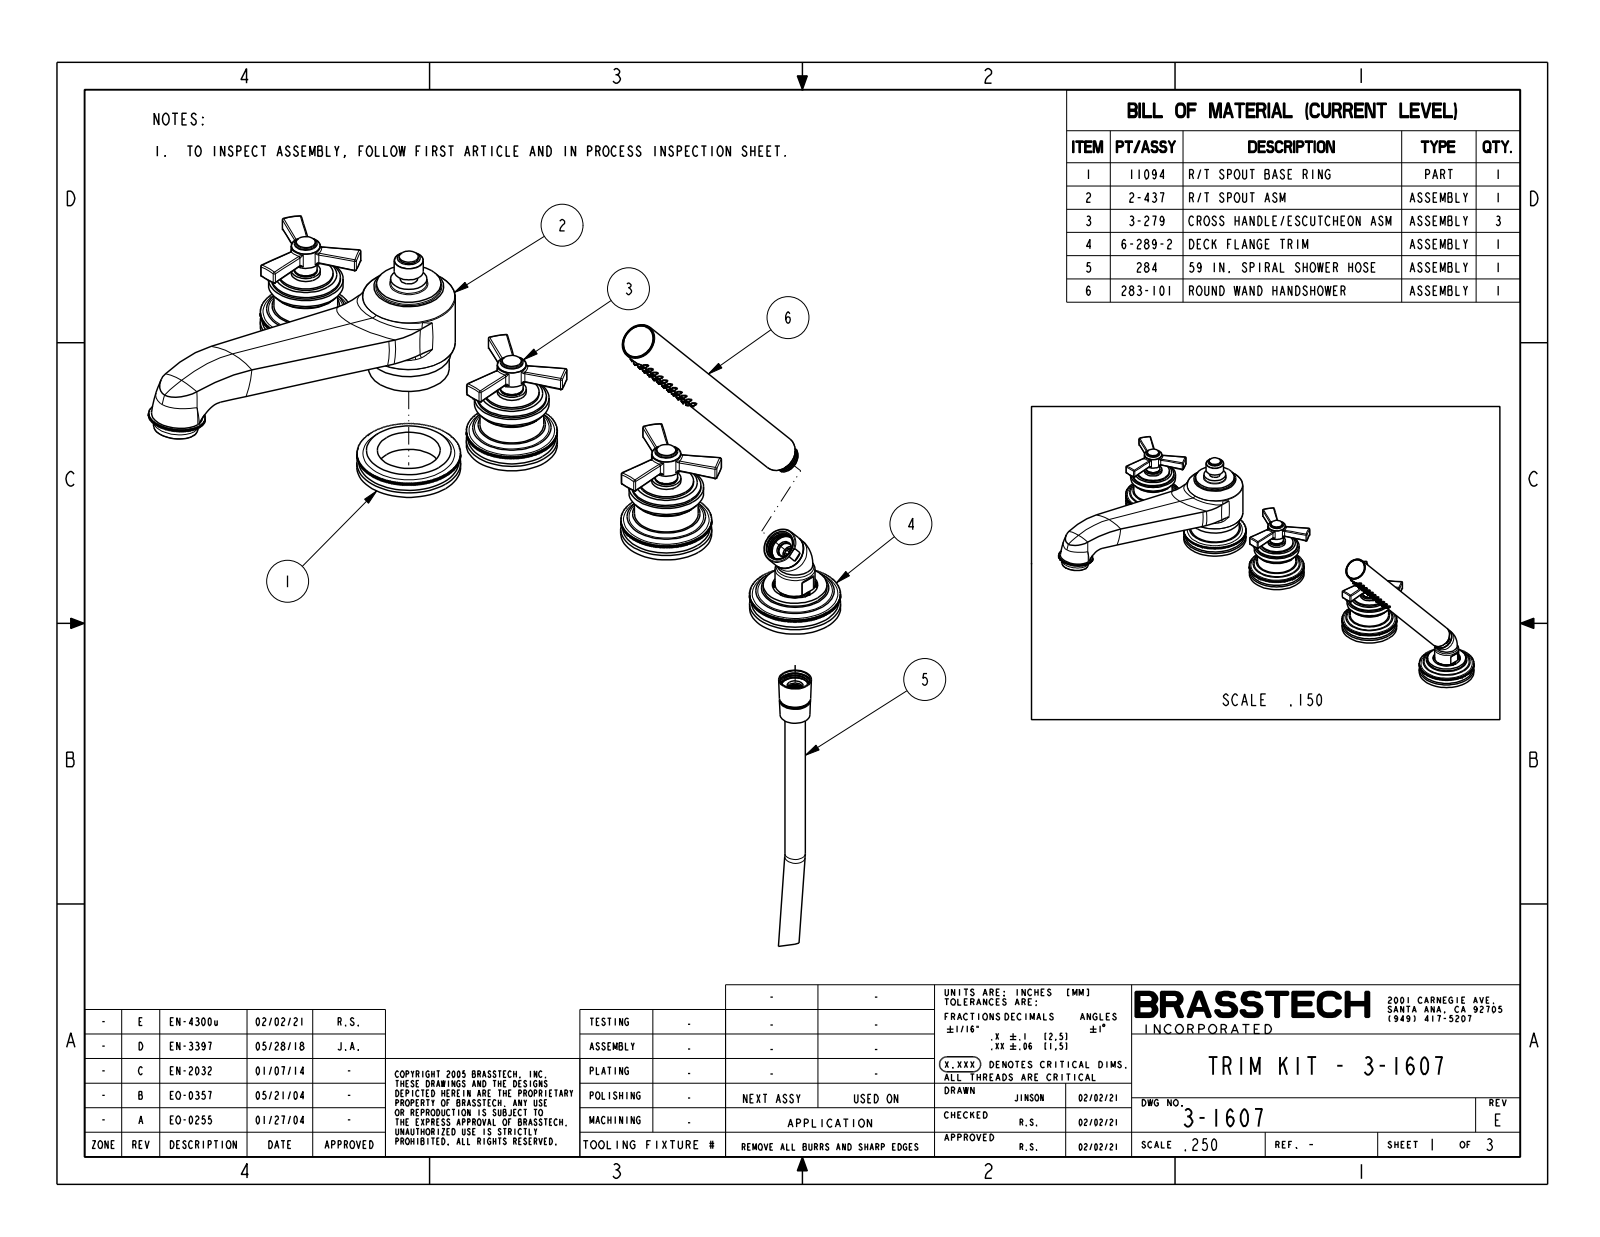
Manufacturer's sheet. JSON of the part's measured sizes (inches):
{"part_name": "3-1607", "step_written_by": "CREO PARAMETRIC BY PTC INC, 2018400 (CONFIG_CONTROL_DESIGN)", "units": "inches", "bodies": {"solids": 6, "faces": 4347, "planar": 2106, "cylindrical": 1346, "other": 895}, "overall_size": [21.67, 11.211, 9.237], "volume_in3": 64.3, "surface_area_in2": 234.3, "round_holes": [[0.14, 44]], "round_bosses_or_shafts": [[2.5, 4], [2.4, 4], [1.75, 4], [0.8, 4], [0.525, 4], [2.05, 3], [1.9, 3], [1.5, 3]], "partial_cylinders_radius": [[0.04, 18], [0.1, 18], [0.05, 6], [0.45, 1], [0.56, 1], [0.781, 1]], "face_to_face_distances": [0.2, 0.1, 1.3, 1.775, 1.1, 0.4, 0.475, 1.375, 1, 1.2], "hole_center_spacings": [0.336, 0.604, 0.17, 0.672, 0.447, 0.29, 0.886, 0.58]}
